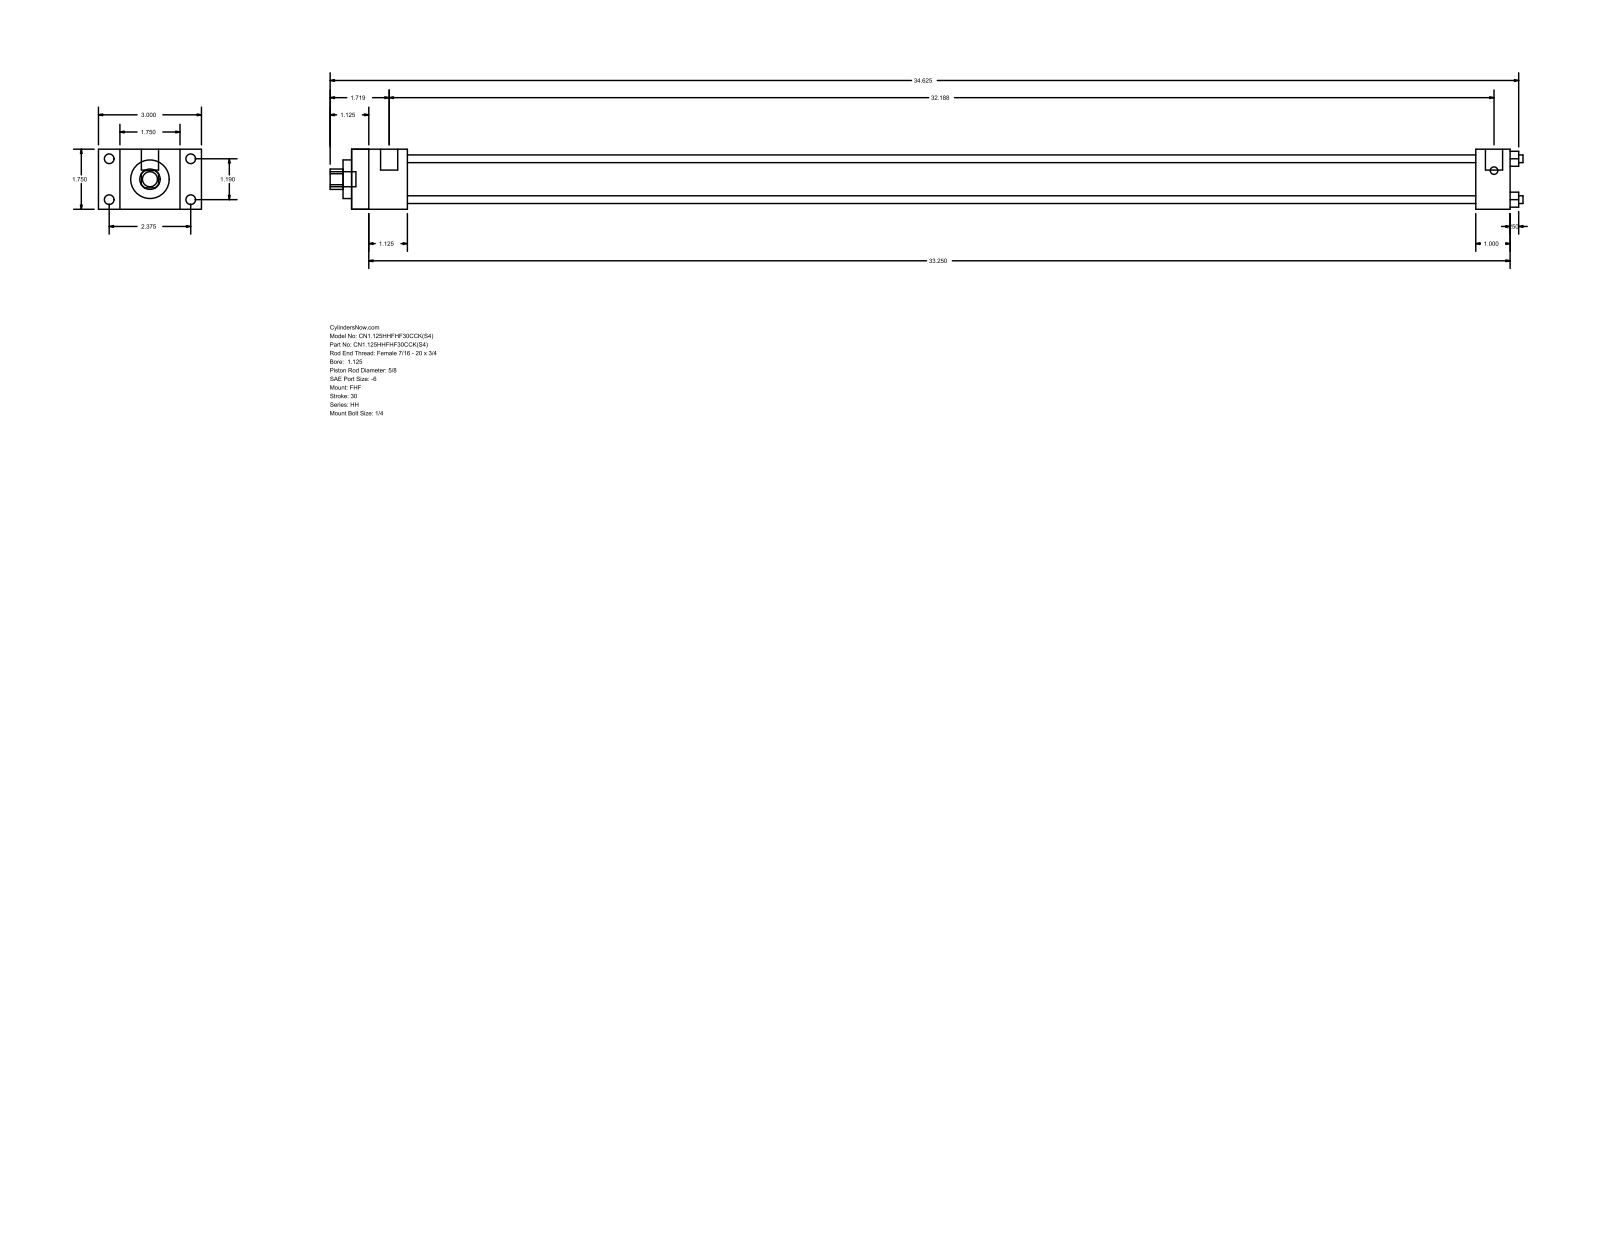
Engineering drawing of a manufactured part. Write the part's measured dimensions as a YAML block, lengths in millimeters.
part_name: "HH_FHF__0112_0.625"
step_written_by: "GSSL Pune (CONFIG_CONTROL_DESIGN)"
units: millimeters
bodies: {solids: 0, faces: 88, planar: 60, cylindrical: 28, other: 0}
overall_size: [882.65, 76.2, 44.45]
round_holes:
  - {diameter: 5.71, count: 4}
  - {diameter: 15.88, count: 1}
  - {diameter: 28.57, count: 1}
  - {diameter: 34.92, count: 1}
round_bosses_or_shafts:
  - {diameter: 7.14, count: 4}
  - {diameter: 5.56, count: 4}
  - {diameter: 12.7, count: 2}
  - {diameter: 11.11, count: 1}
partial_cylinders:
  - {radius: 7.54, count: 1}
face_to_face_distances: [44.46, 15.87, 60.33, 41.27, 76.2, 857.24, 815.97, 831.85, 790.58, 25.39]
hole_center_spacings: [21.37, 30.22, 42.74]
